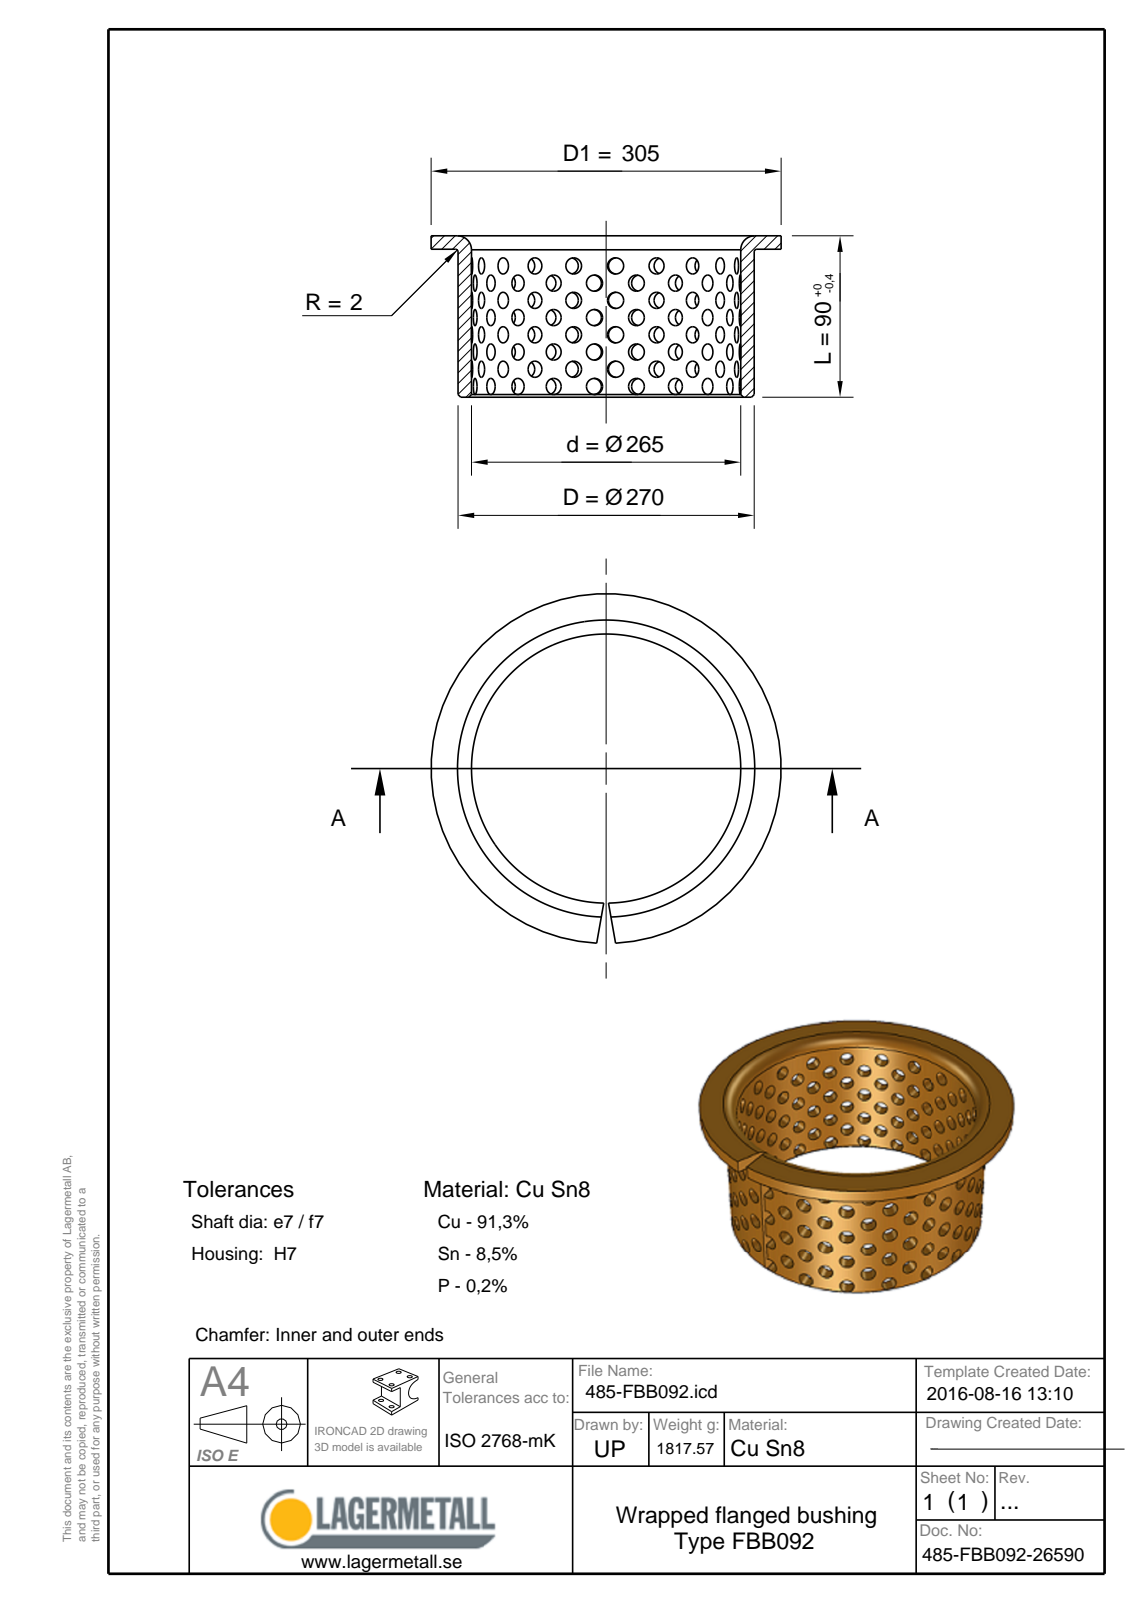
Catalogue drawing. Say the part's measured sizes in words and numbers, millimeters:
The part is named "485-FBB092-26590". Its 3-D file was written by "Spatial InterOp 3D (CONFIG_CONTROL_DESIGN)". It is 1 solid with 12 faces: 5 planar, 3 cylindrical and 4 other. Overall it measures 305 by 304.95 by 90 millimeters. Its volume is 224 392 cubic millimeters and its surface area 184 293 square millimeters. Round holes: 1 of diameter 265. Round bosses or shafts: 1 of diameter 305, 1 of diameter 270. The main face-to-face distances are 2.5, 87.5, 90.
